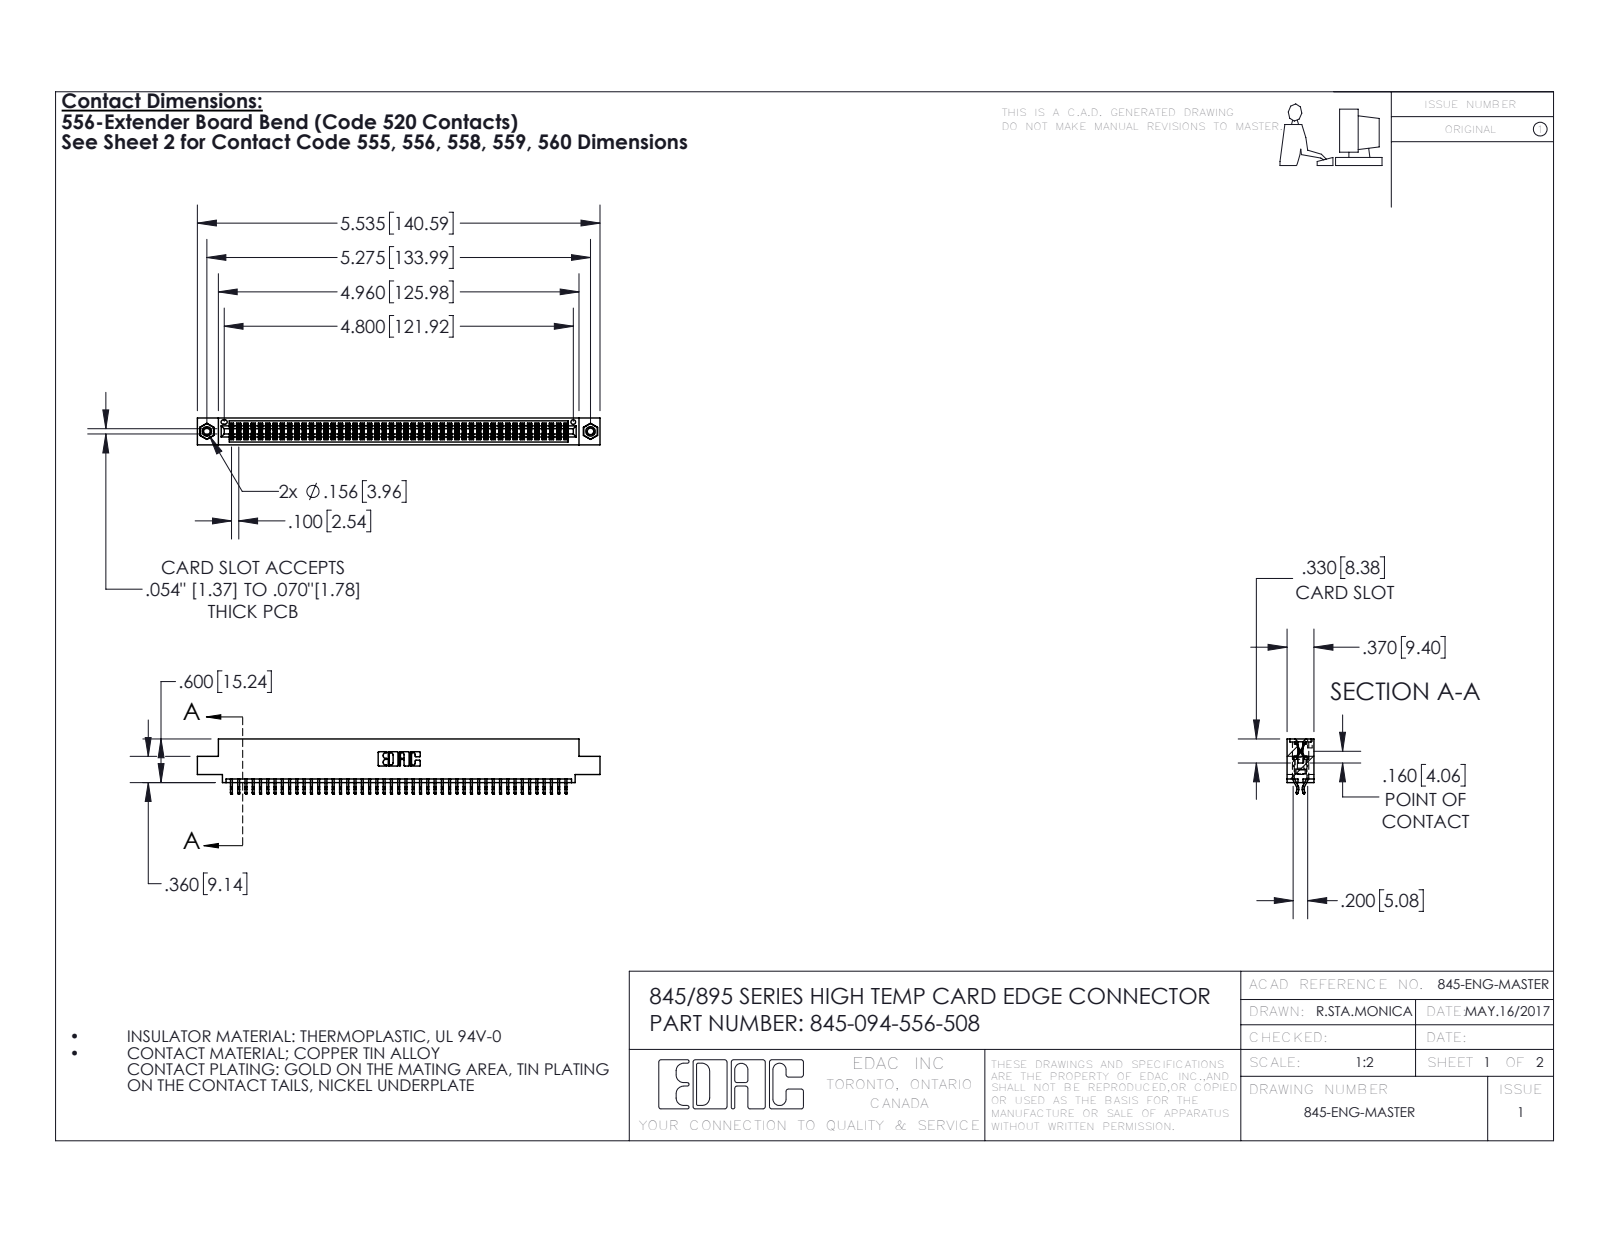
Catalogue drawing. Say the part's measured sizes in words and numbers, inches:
The part is named "345-250-001_345-250-003-102; 345-094-556-508; 345-292-001_556 Tail; 345 Part_0.110 Offset - 0.156 Dia-TI". Its 3-D file was written by "SolidWorks 2016 (CONFIG_CONTROL_DESIGN)". It is 97 solids with 5454 faces: 3594 planar, 1844 cylindrical and 16 other. Overall it measures 5.535 by 0.757 by 0.37 inches. Its volume is 0.831 cubic inches and its surface area 31.39 square inches. Round holes: 2 of diameter 0.089, 2 of diameter 0.125, 2 of diameter 0.156, 1 of diameter 0.064. Round bosses or shafts: 2 of diameter 0.155. Partial cylindrical surfaces (rounded edges, fillets, slot ends): 141 of radius 0.006, 22 of radius 0.01, 6 of radius 0.007, 6 of radius 0.031, 3 of radius 0.026, 2 of radius 0.01, 2 of radius 0.014, 2 of radius 0.019. The main face-to-face distances are 0.072, 0.298, 0.37, 0.2, 0.025, 0.098, 0.272, 0.225, 0.175, 0.149. The hole center spacings are 0.27, 5.039, 5.275.
